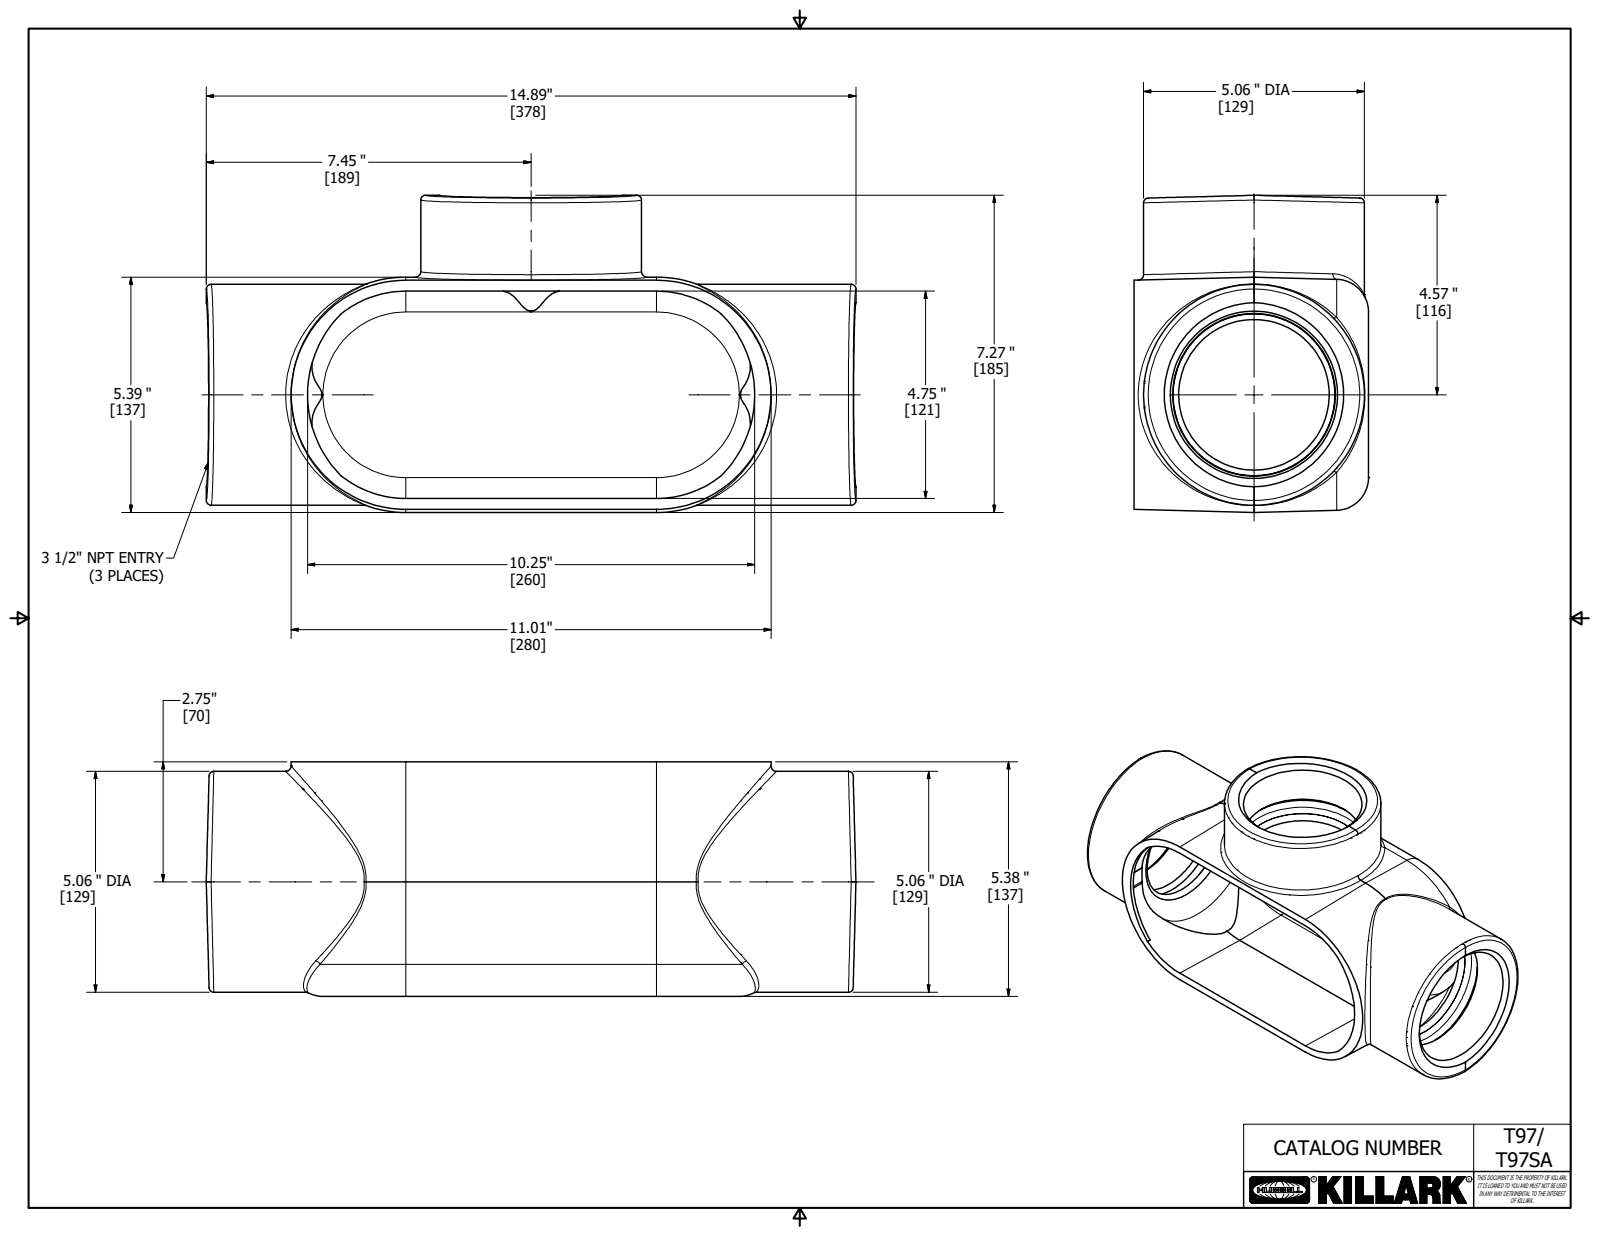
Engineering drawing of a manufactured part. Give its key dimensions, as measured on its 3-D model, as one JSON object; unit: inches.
{"part_name": "17744", "step_written_by": "Autodesk Inventor 2018 (AUTOMOTIVE_DESIGN)", "units": "inches", "bodies": {"solids": 1, "faces": 118, "planar": 34, "cylindrical": 26, "other": 58}, "overall_size": [14.894, 7.269, 5.375], "volume_in3": 89.82, "surface_area_in2": 511.2, "round_holes": [[4.011, 2]], "round_bosses_or_shafts": [[5.062, 2]], "partial_cylinders_radius": [[0.05, 4], [0.125, 4], [0.5, 2], [0.75, 2], [2.375, 2]], "face_to_face_distances": [0.25, 5.144, 4.894, 5.375, 5.125, 5.394, 14.894, 7.269, 7.019, 2.125]}
